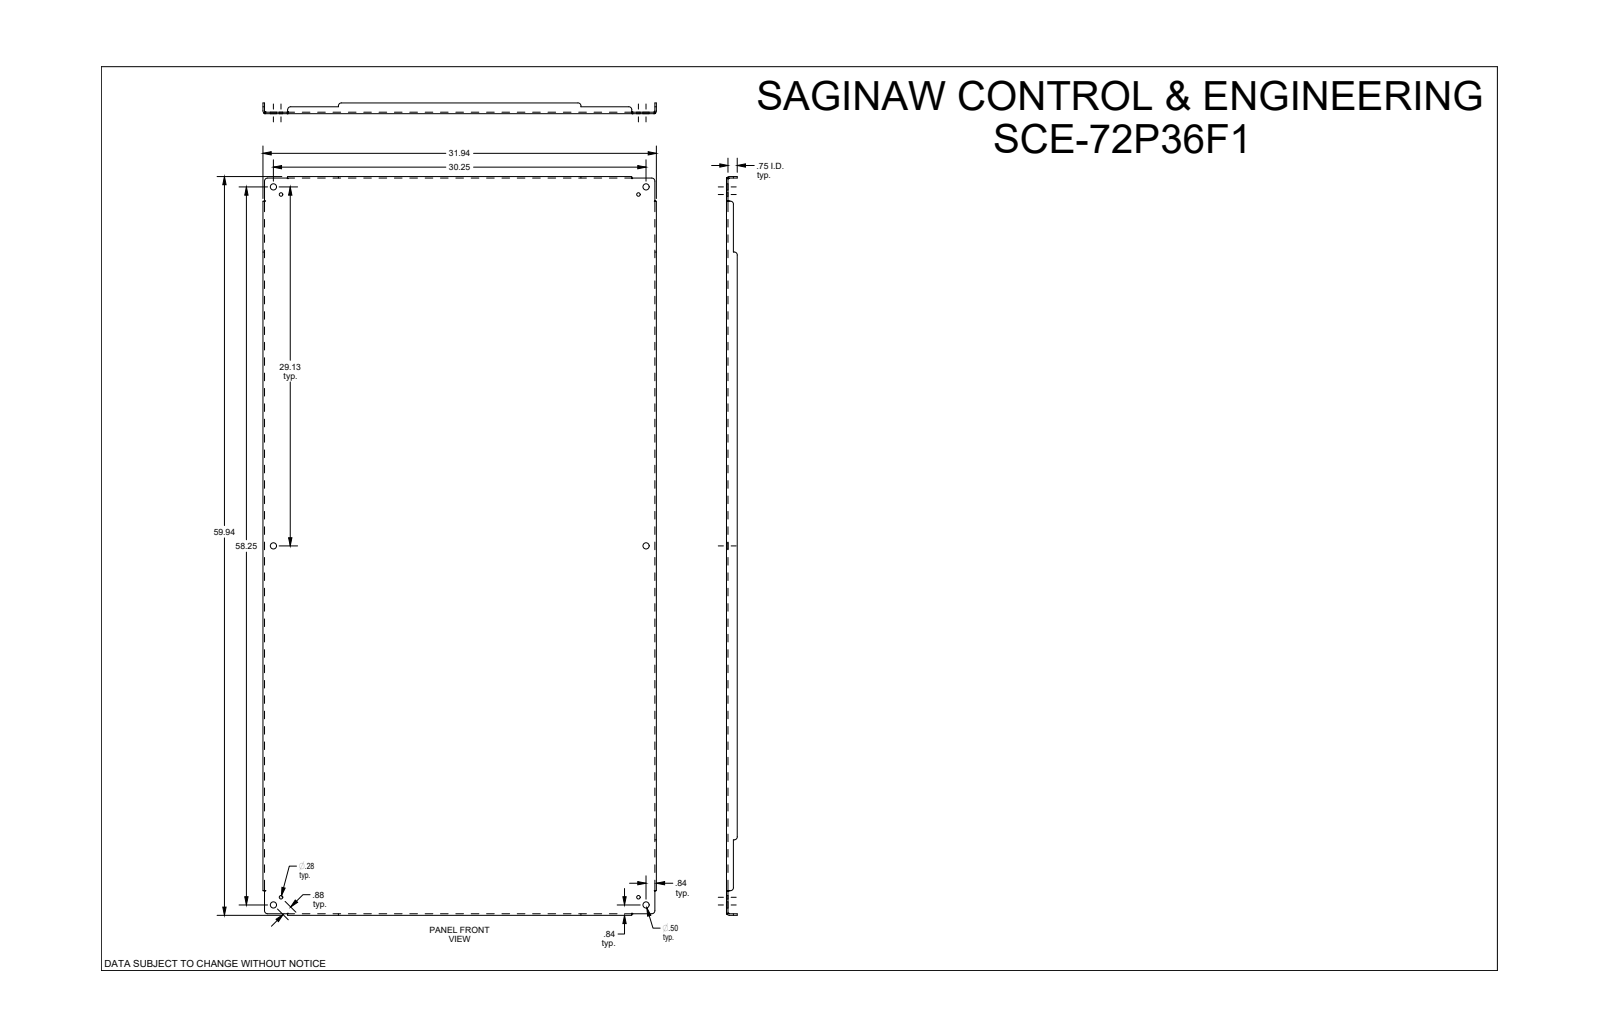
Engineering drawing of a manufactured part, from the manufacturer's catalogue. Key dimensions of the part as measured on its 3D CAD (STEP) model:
Part name (STEP PRODUCT): SCE-72P36F1
STEP written by: SolidWorks 2019 (CONFIG_CONTROL_DESIGN)
Units: inches
Bodies: 1 solid, 108 faces (46 planar, 38 cylindrical, 24 other)
Overall size (bounding box): 59.938 × 31.938 × 0.875
Volume: 251.7 in³ · Surface area: 4 052 in²
Round holes (diameter × count): ⌀0.5 ×6, ⌀0.281 ×4
Partial cylindrical surfaces — rounded edges, fillets, slot ends (radius × count): R0.25 ×12, R0.112 ×4, R0.237 ×4
Main face-to-face distances: 0.125, 0.125, 31.813, 31.687, 31.938, 59.813, 0.75, 0.875, 59.687, 59.938
Hole centre spacings: 0.875, 28.513, 29.125, 29.637, 41.117, 41.992, 57.634, 64.802
